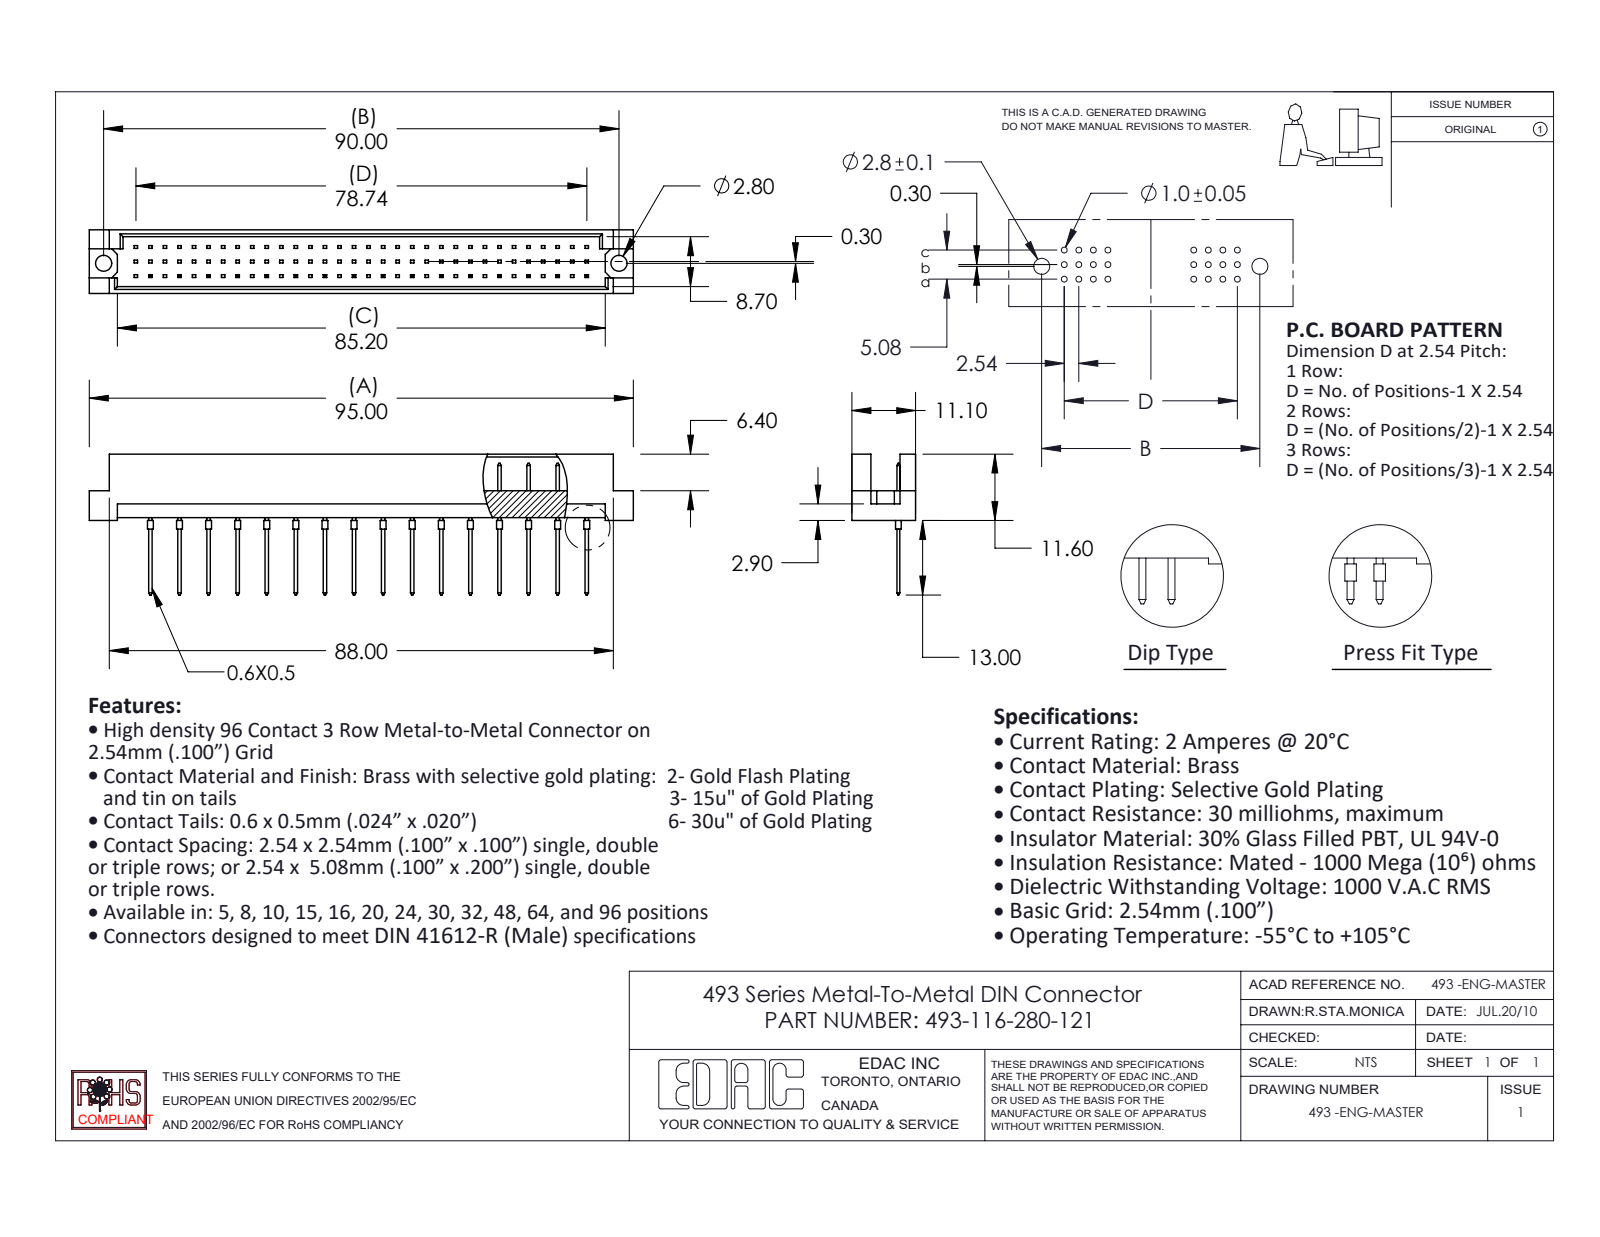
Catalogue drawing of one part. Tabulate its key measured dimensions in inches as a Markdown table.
| quantity | value |
| --- | --- |
| part name | 493-290_80; 493-116-280-122; 493 Part_96 |
| STEP written by | SolidWorks 2020 (CONFIG_CONTROL_DESIGN) |
| units | inches |
| bodies | 17 solids, 788 faces (752 planar, 36 cylindrical, 0 other) |
| overall size | 3.74 × 0.969 × 0.437 |
| volume | 0.353 in³ |
| surface area | 11.34 in² |
| round holes (diameter × count) | 0.11 × 2 |
| round bosses / shafts (diameter × count) | 0.039 × 16 |
| main face-to-face distances | 0.047, 0.39, 0.437, 0.343, 0.185, 0.02, 0.2, 0.109, 0.128, 0.309 |
| hole center spacings | 3.543 |
